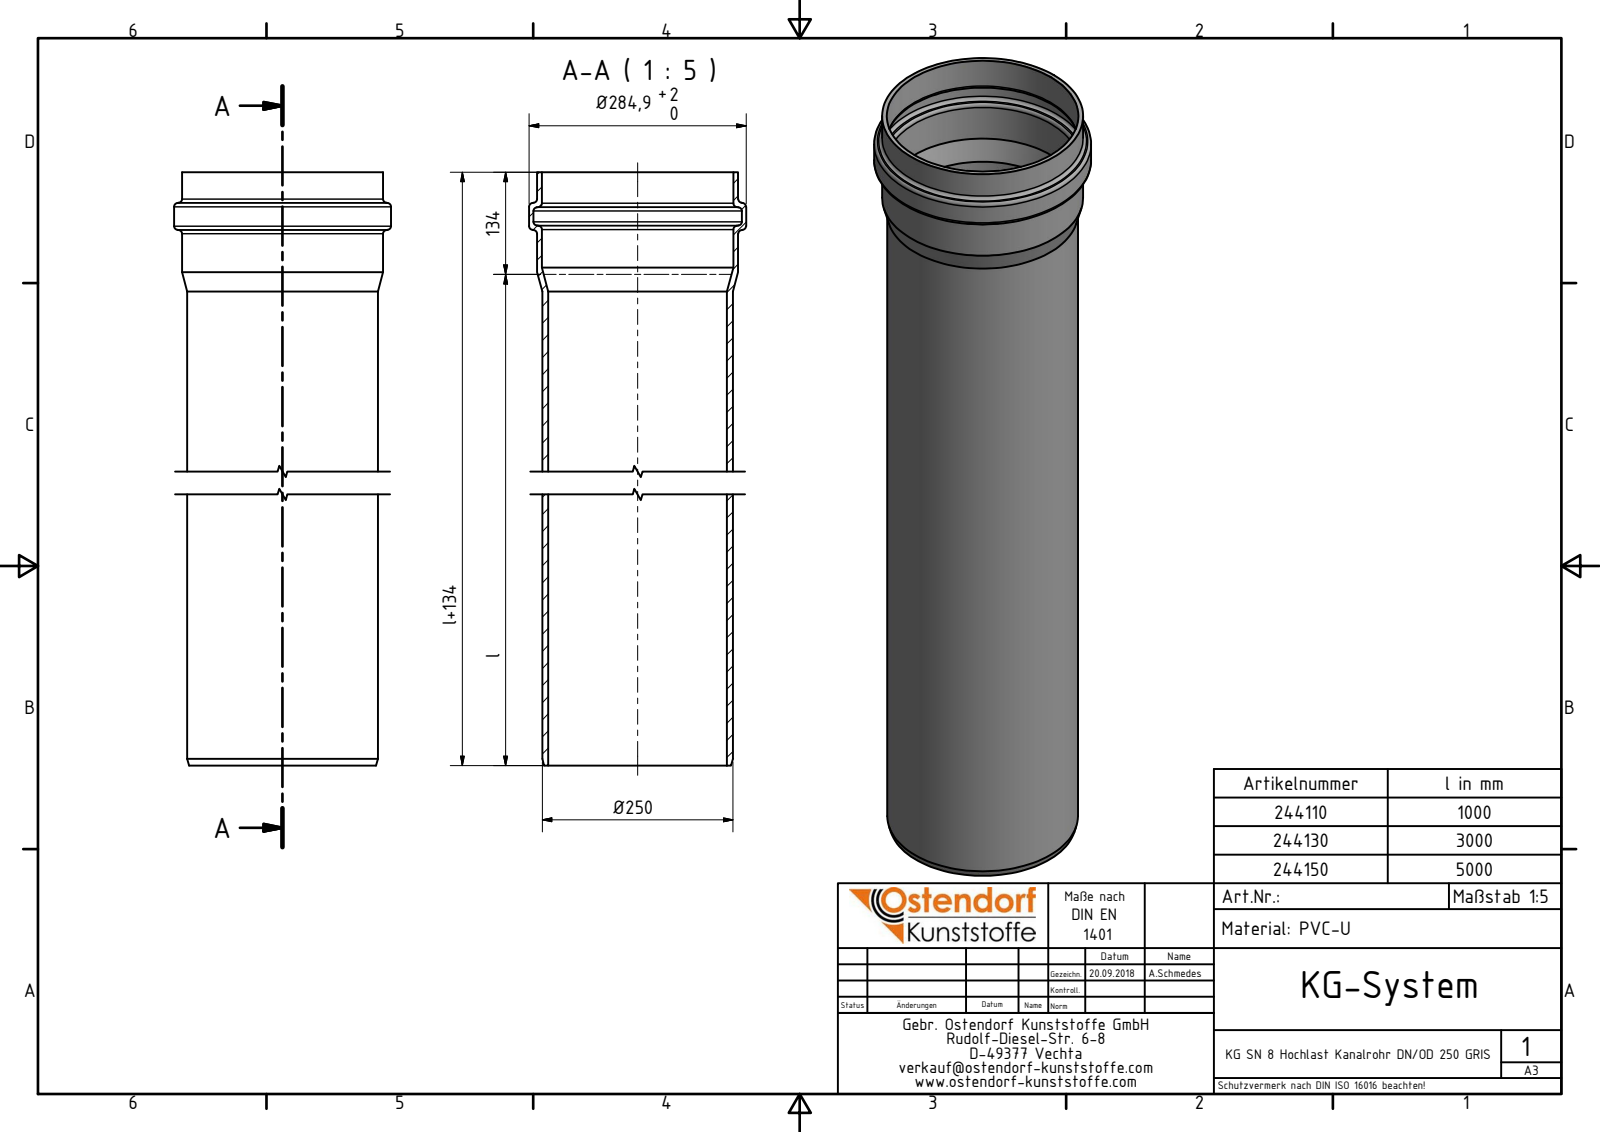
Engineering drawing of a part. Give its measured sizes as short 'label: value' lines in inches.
name: 244110 KGEM Passlängen SN 8 DN_OD 250x1000 GRIS
written by: Autodesk Inventor 2016 (AUTOMOTIVE_DESIGN)
unit: in
bodies: 1 solid, 25 faces (2 planar, 8 cylindrical, 15 other)
size: 44.646 × 11.217 × 11.217
volume: 409.7 in³; area: 2 756 in²
holes: 1× ⌀9.238, 1× ⌀9.902, 1× ⌀10.783
bosses: 1× ⌀11.217, 1× ⌀10.39, 1× ⌀9.852
face distances: 44.646
